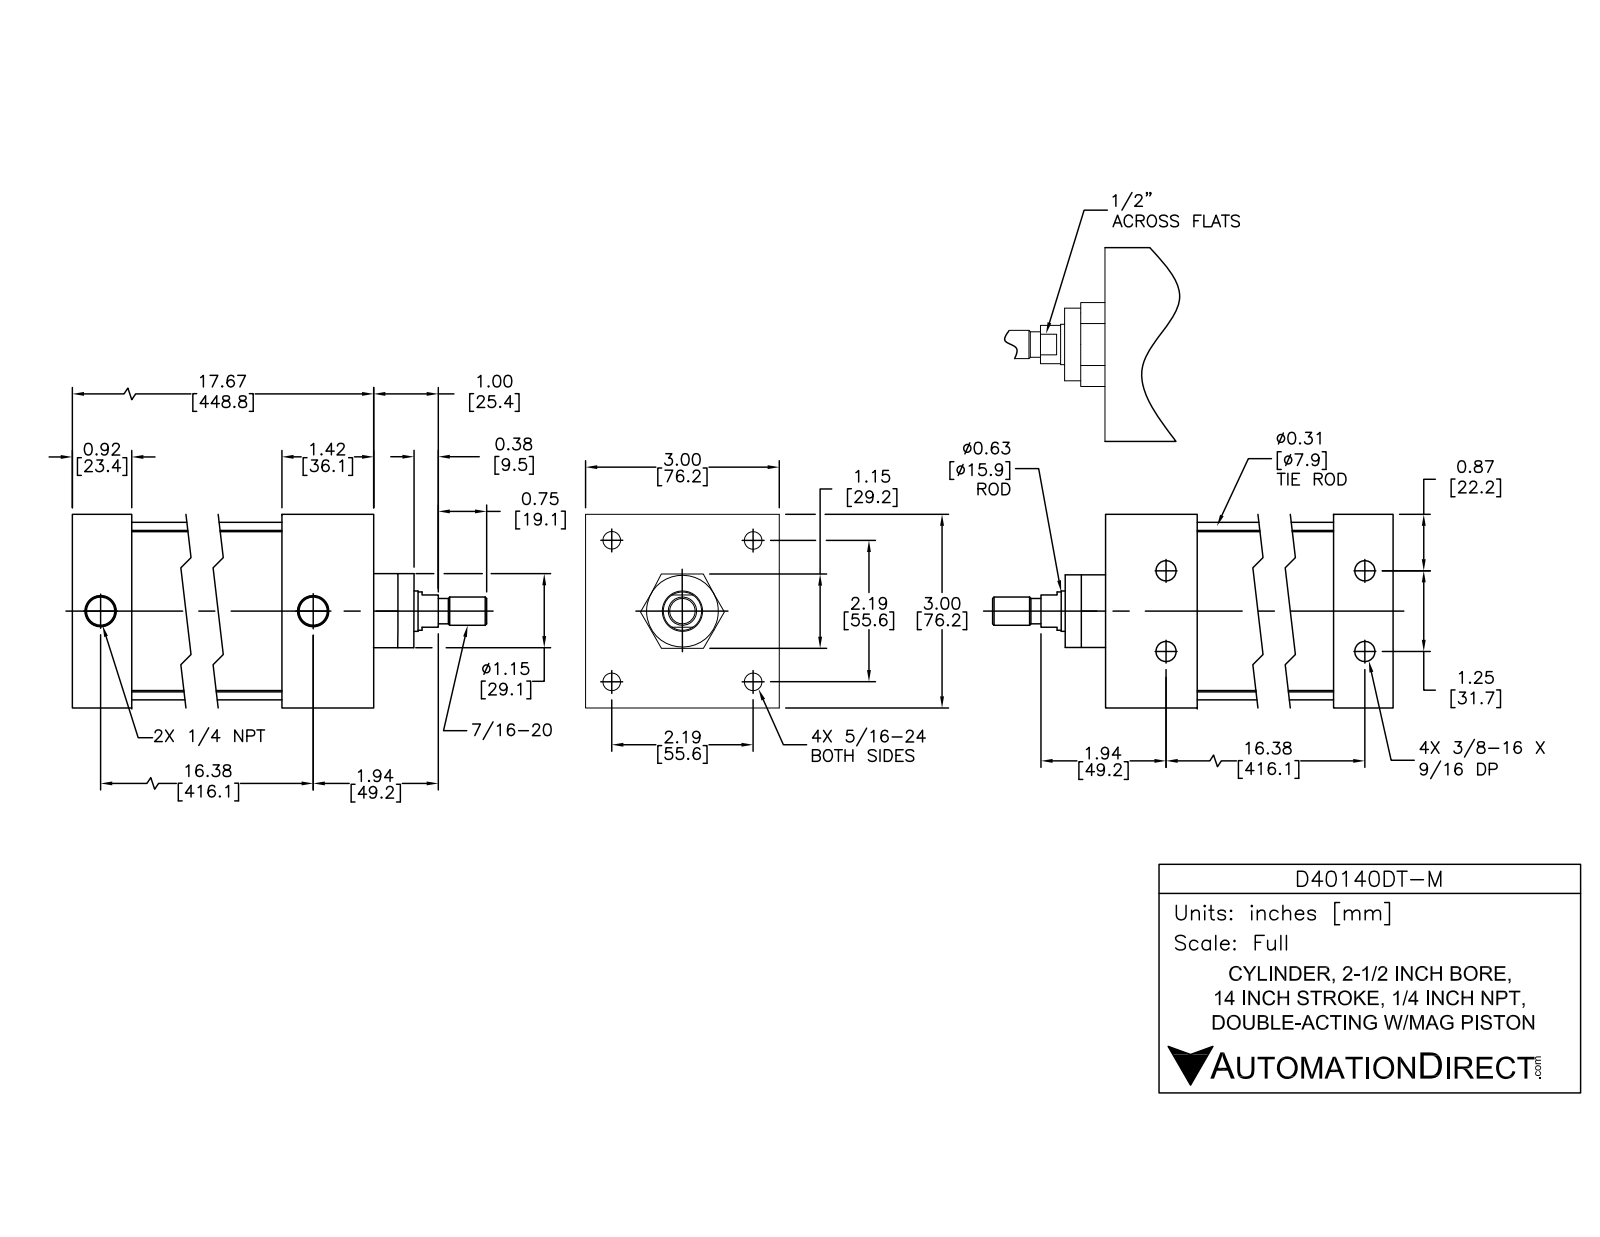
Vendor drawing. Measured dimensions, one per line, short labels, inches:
name: D40140DT-M BODY; D40140DT-M PISTON; D40140DT-M
written by: SolidWorks 2015 (AUTOMOTIVE_DESIGN)
unit: in
bodies: 12 solids, 298 faces (94 planar, 114 cylindrical, 90 other)
size: 19.496 × 3 × 3
volume: 51.4 in³; area: 460.6 in²
holes: 4× ⌀0.267, 4× ⌀0.307, 4× ⌀0.359, 4× ⌀0.5, 2× ⌀0.297, 2× ⌀0.477, 1× ⌀0.625, 1× ⌀0.628, 1× ⌀2.5
bosses: 4× ⌀0.484, 4× ⌀0.313, 4× ⌀0.282, 1× ⌀2.75, 1× ⌀2.497, 1× ⌀1.12, 1× ⌀0.622, 1× ⌀0.59
rounds: 4× R0.3
face distances: 3, 0.08, 15.326, 17.746, 16.726, 1.02, 1.42, 15.306, 16.326, 1
hole spacings: 1.556, 2.2, 16.382, 16.37, 0.625, 0.625, 1.25, 3.111
